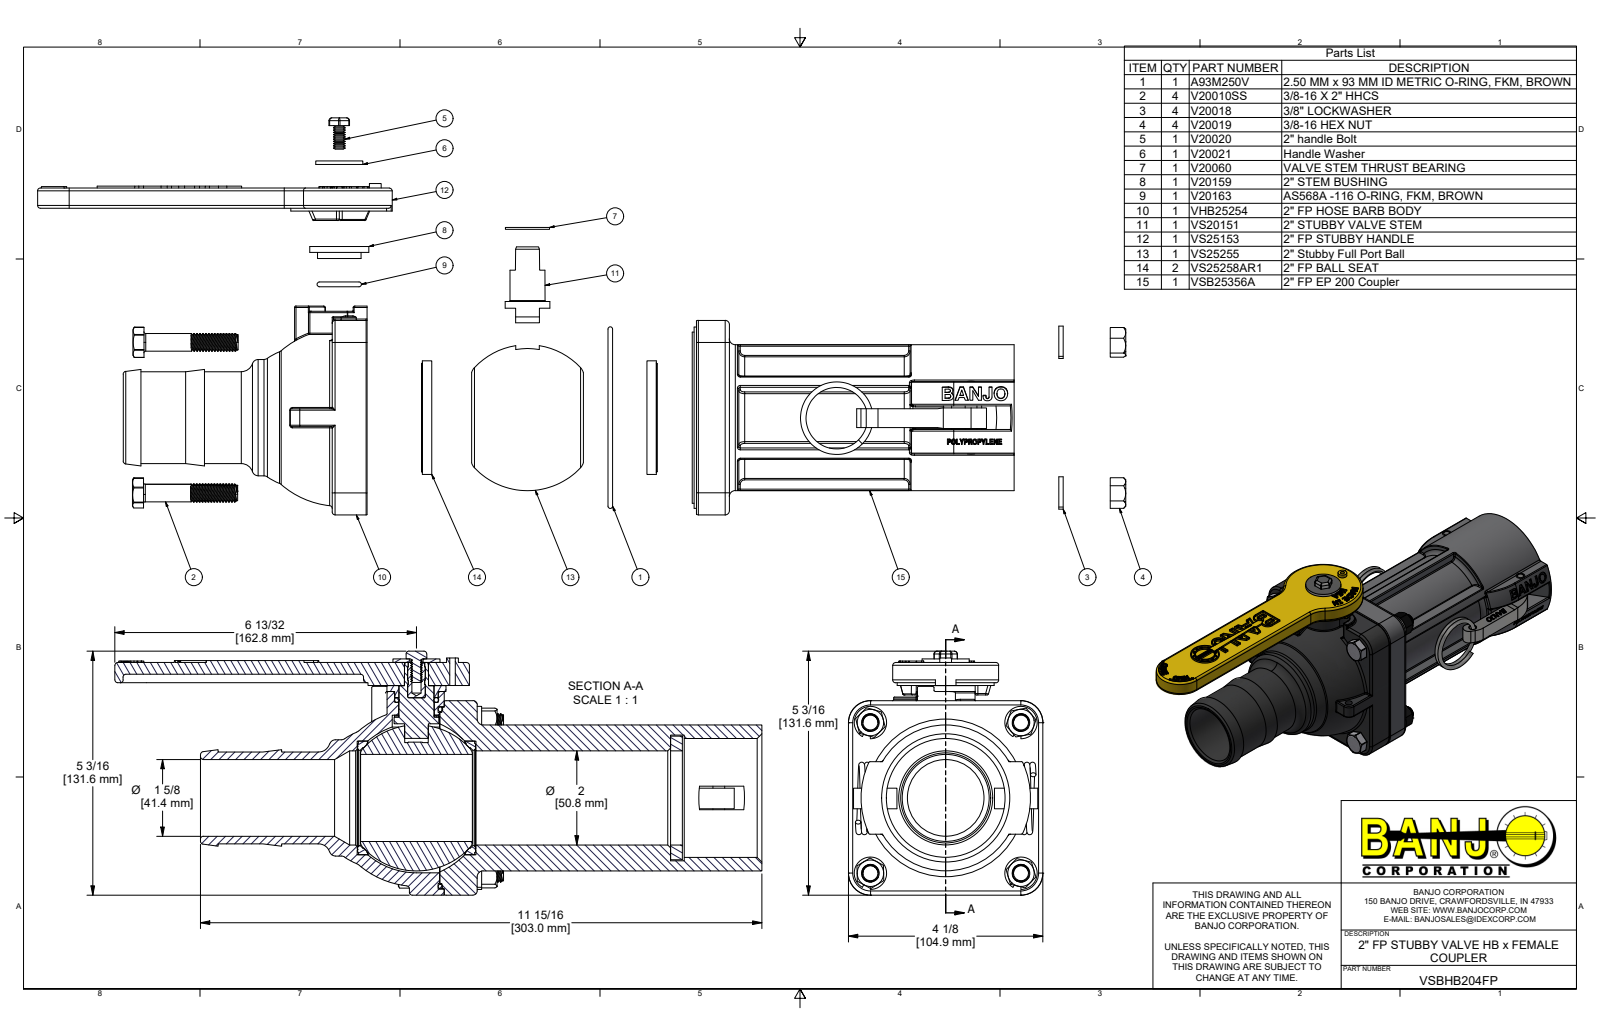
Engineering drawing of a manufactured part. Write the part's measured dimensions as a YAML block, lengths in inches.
part_name: "VSBHB204FP; VHB25254; VHB25254X; VS20151 (+8 more)"
step_written_by: "Autodesk Inventor 2019 (AUTOMOTIVE_DESIGN)"
units: inches
bodies: {solids: 33, faces: 3176, planar: 1156, cylindrical: 751, other: 1269}
overall_size: [13.72, 5.182, 4.13]
volume: 54.74
surface_area: 420.1
round_holes:
  - {diameter: 0.307, count: 4}
  - {diameter: 0.385, count: 4}
  - {diameter: 0.406, count: 4}
  - {diameter: 0.44, count: 4}
  - {diameter: 0.195, count: 2}
  - {diameter: 0.2, count: 2}
  - {diameter: 0.25, count: 2}
  - {diameter: 0.258, count: 2}
  - {diameter: 0.118, count: 1}
  - {diameter: 0.196, count: 1}
  - {diameter: 0.281, count: 1}
  - {diameter: 0.351, count: 1}
round_bosses_or_shafts:
  - {diameter: 0.324, count: 60}
  - {diameter: 0.687, count: 4}
  - {diameter: 0.375, count: 4}
  - {diameter: 0.26, count: 2}
  - {diameter: 0.249, count: 2}
  - {diameter: 3.85, count: 1}
  - {diameter: 3.635, count: 1}
  - {diameter: 3.625, count: 1}
partial_cylinders:
  - {radius: 0.03, count: 89}
  - {radius: 0.06, count: 30}
  - {radius: 0.02, count: 12}
  - {radius: 0.09, count: 8}
  - {radius: 0.162, count: 8}
  - {radius: 0.32, count: 4}
  - {radius: 0.468, count: 4}
  - {radius: 0.469, count: 4}
face_to_face_distances: [0.25, 0.7, 4.13, 4.11, 4.81, 1.44, 1.94, 4.691, 4.941, 5.55]
hole_center_spacings: [2.263, 3.2, 2.041, 2.176, 2.457, 3.861, 3.898, 4.293]
